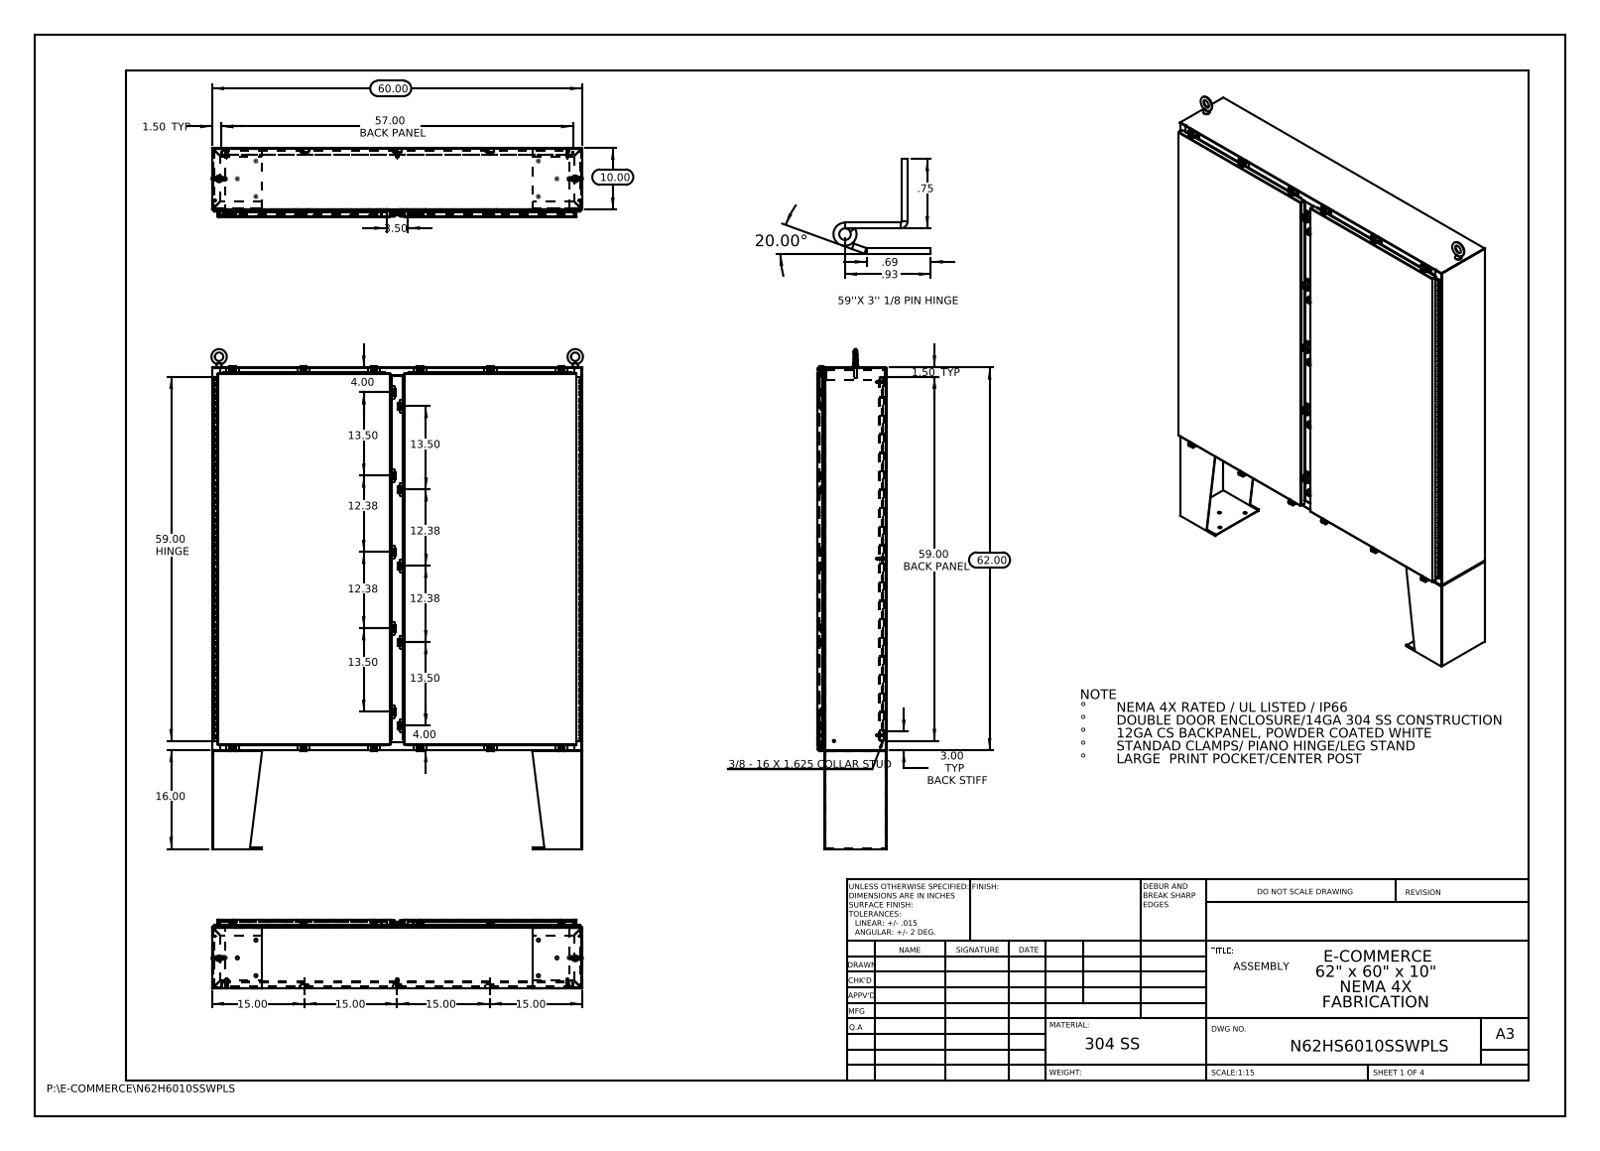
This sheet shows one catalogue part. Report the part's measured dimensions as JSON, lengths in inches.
{"part_name": "Clamp Bracket; N62H6010SSWPLS Hinge_DoubleDoor; Quarter-20 CD Stud; N62H6010SSWPLS Body (+8 more)", "step_written_by": "SolidWorks 2013 (CONFIG_CONTROL_DESIGN)", "units": "inches", "bodies": {"solids": 144, "faces": 6444, "planar": 3354, "cylindrical": 2762, "other": 328}, "overall_size": [81, 60.226, 11.201], "volume_in3": 1356, "surface_area_in2": 32852, "round_holes": [[0.213, 22], [0.26, 22], [0.5, 14], [0.75, 4], [0.125, 2], [0.125, 2]], "round_bosses_or_shafts": [[0.25, 24], [0.5, 22], [0.399, 22], [0.625, 10], [0.375, 8], [0.33, 8], [0.315, 3], [0.236, 3]], "partial_cylinders_radius": [[0.06, 96], [0.013, 48], [0.12, 44], [0.141, 44], [0.088, 40], [0.05, 32], [0.08, 32], [0.09, 32]], "face_to_face_distances": [0.075, 11.126, 0.104, 1.075, 11.051, 1, 10.126, 11.201, 10.051, 1.179], "hole_center_spacings": [61.431, 68.531, 2.608, 4.158, 4.293, 6.626, 6.647, 11.437]}
